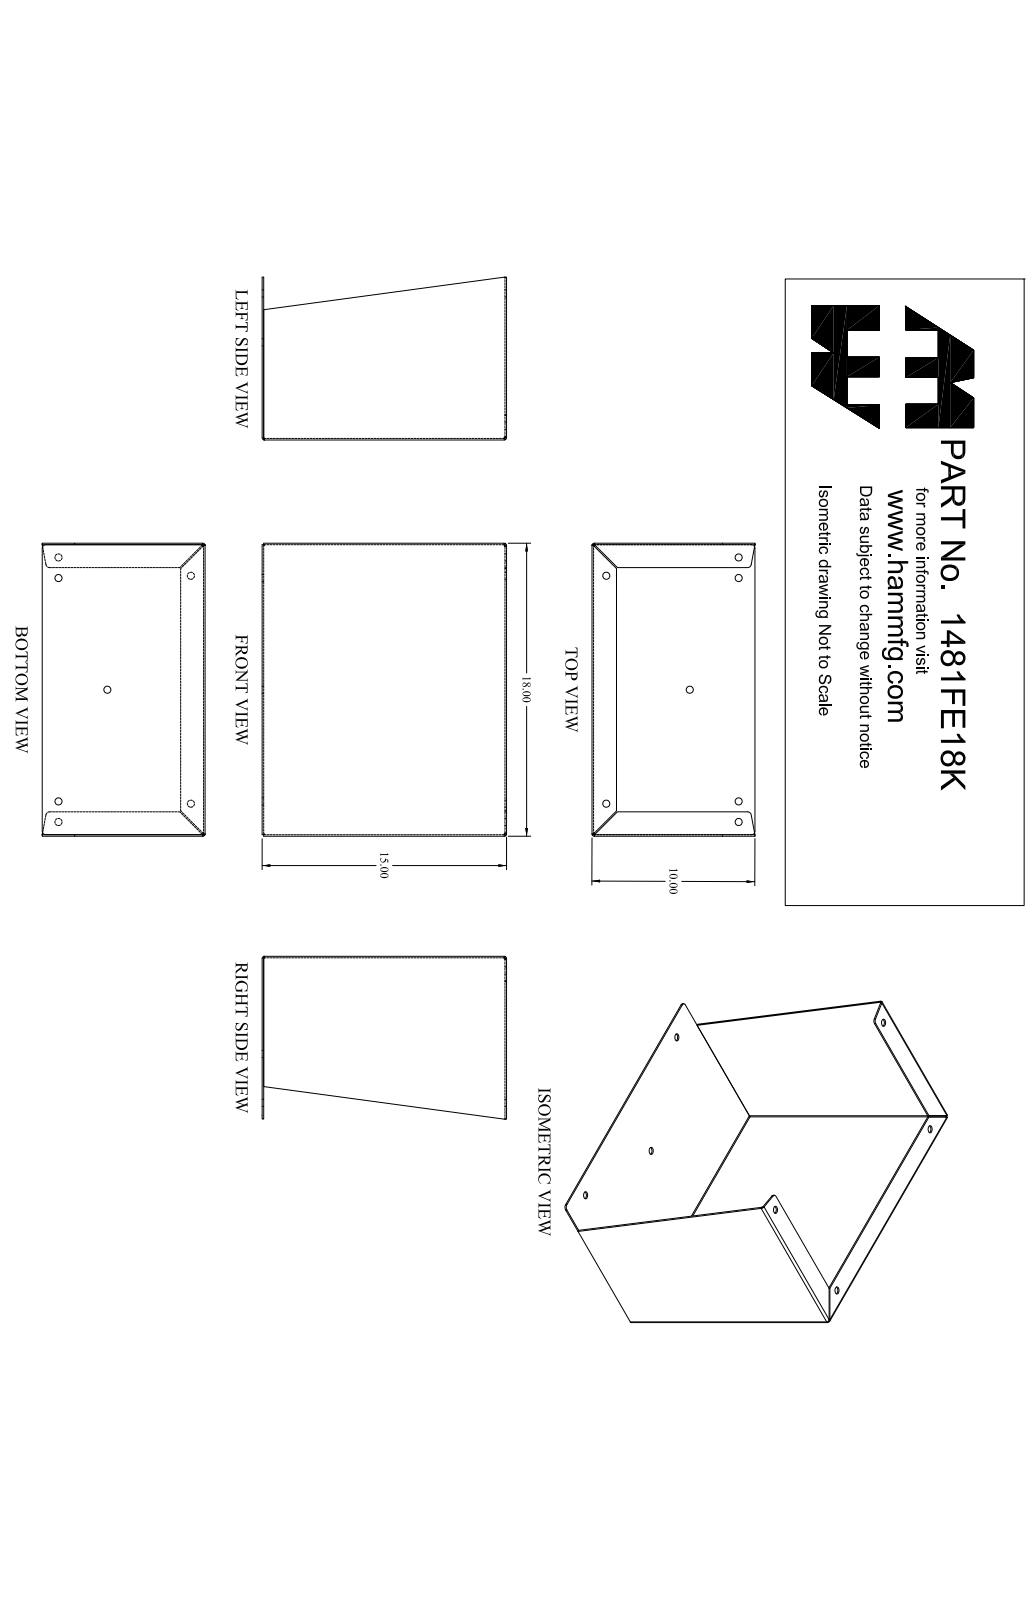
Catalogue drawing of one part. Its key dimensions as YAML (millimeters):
part_name: "1481FE18K_Default"
step_written_by: "SolidWorks 2019 (CONFIG_CONTROL_DESIGN)"
units: millimeters
bodies: {solids: 1, faces: 78, planar: 42, cylindrical: 30, other: 6}
overall_size: [457.2, 381, 254]
volume: 1177000
surface_area: 983200
round_holes:
  - {diameter: 11.1, count: 7}
partial_cylinders:
  - {radius: 1.2, count: 6}
  - {radius: 3.6, count: 6}
  - {radius: 5.6, count: 4}
face_to_face_distances: [2.4, 454.8, 2.4, 452.4, 457.2, 381, 376.2, 378.6, 378.6, 35.7]
hole_center_spacings: [190.2, 206.4, 208.3, 220.3, 408.1, 32.2, 32.2, 220]
